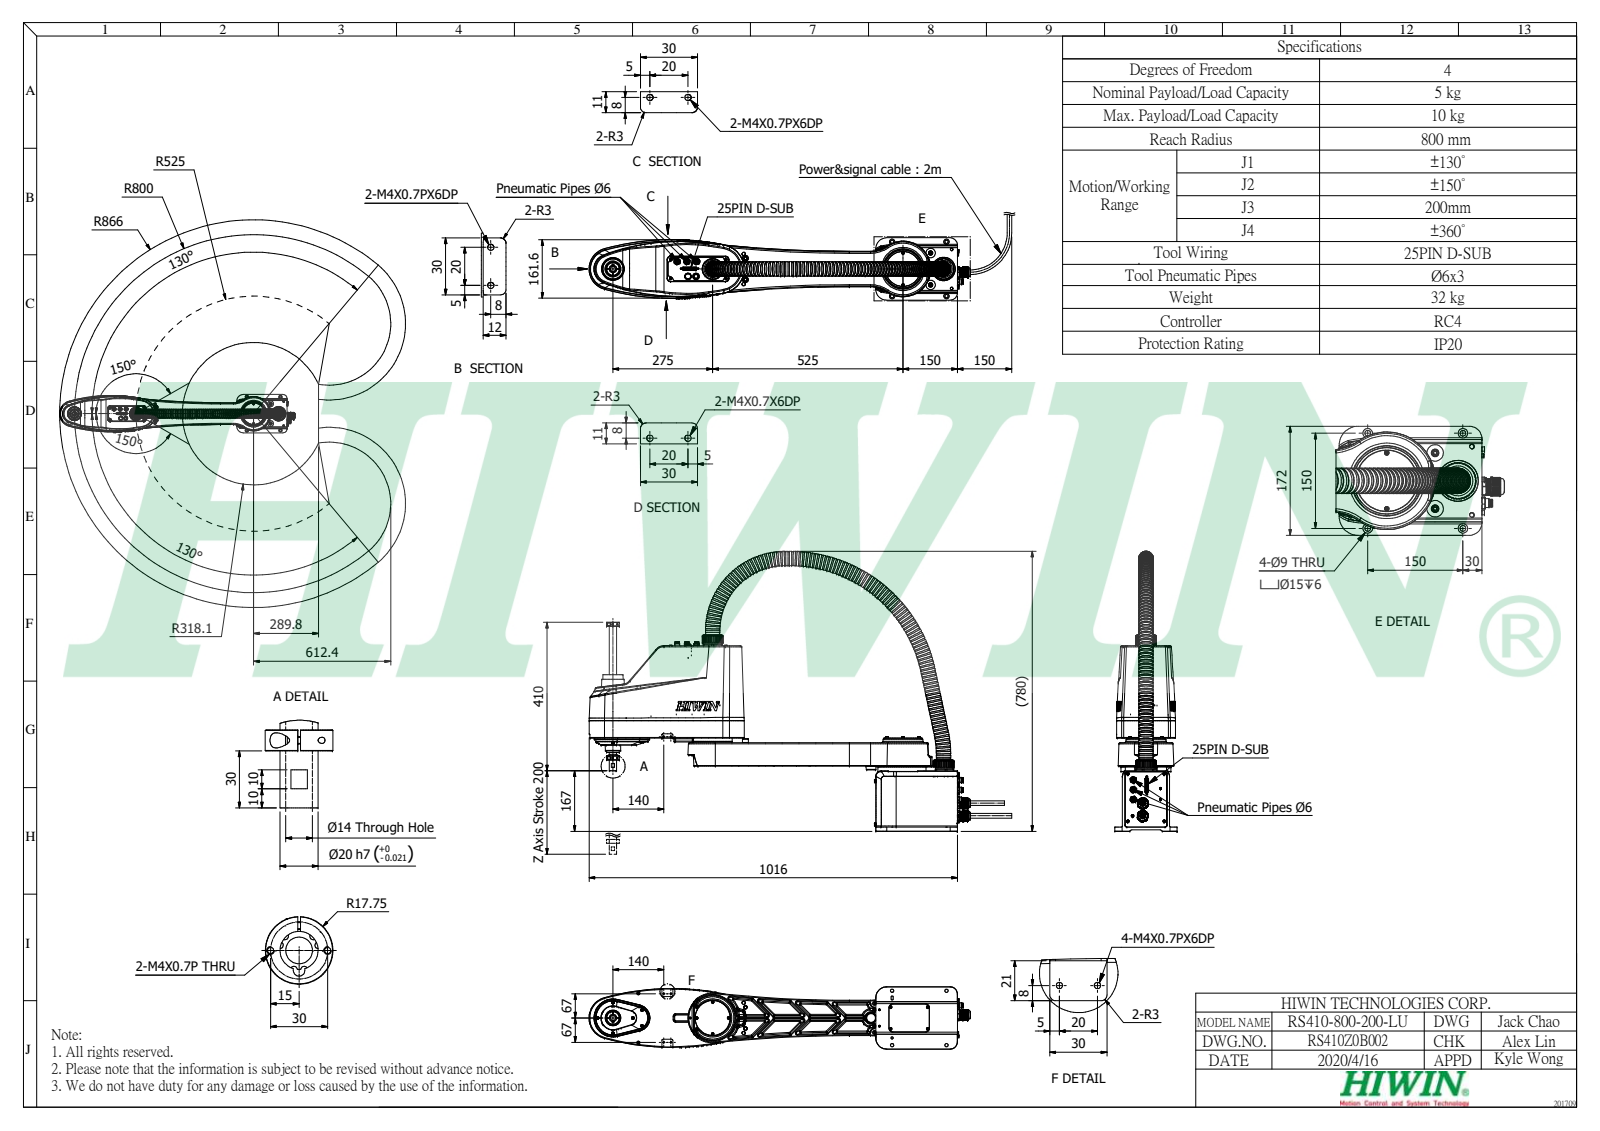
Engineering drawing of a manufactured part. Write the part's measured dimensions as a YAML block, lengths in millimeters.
part_name: "RS410-800-200-LU; RS410-1; A; B-800 (+1 more)"
step_written_by: "Autodesk Inventor 2020 (AUTOMOTIVE_DESIGN)"
units: millimeters
bodies: {solids: 86, faces: 3430, planar: 1627, cylindrical: 899, other: 904}
overall_size: [1051.52, 771.12, 172]
volume: 22670000
surface_area: 1635000
round_holes:
  - {diameter: 3.3, count: 10}
  - {diameter: 3.24, count: 8}
  - {diameter: 4.5, count: 8}
  - {diameter: 9, count: 8}
  - {diameter: 11, count: 8}
  - {diameter: 8.38, count: 6}
  - {diameter: 4, count: 2}
  - {diameter: 33.5, count: 2}
  - {diameter: 81.2, count: 2}
  - {diameter: 15, count: 1}
  - {diameter: 17.2, count: 1}
  - {diameter: 20, count: 1}
round_bosses_or_shafts:
  - {diameter: 40, count: 97}
  - {diameter: 38, count: 97}
  - {diameter: 7, count: 55}
  - {diameter: 4, count: 31}
  - {diameter: 5.5, count: 20}
  - {diameter: 12, count: 8}
  - {diameter: 10, count: 8}
  - {diameter: 14, count: 6}
partial_cylinders:
  - {radius: 3, count: 51}
  - {radius: 2, count: 36}
  - {radius: 0.2, count: 27}
  - {radius: 5, count: 25}
  - {radius: 4, count: 21}
  - {radius: 1.98, count: 20}
  - {radius: 1.5, count: 18}
  - {radius: 0.8, count: 11}
face_to_face_distances: [2, 49, 13, 12, 51, 130, 10, 61, 63, 70]
hole_center_spacings: [21, 25.88, 63.91, 16.07, 38.8, 40.86, 62.23, 20]
